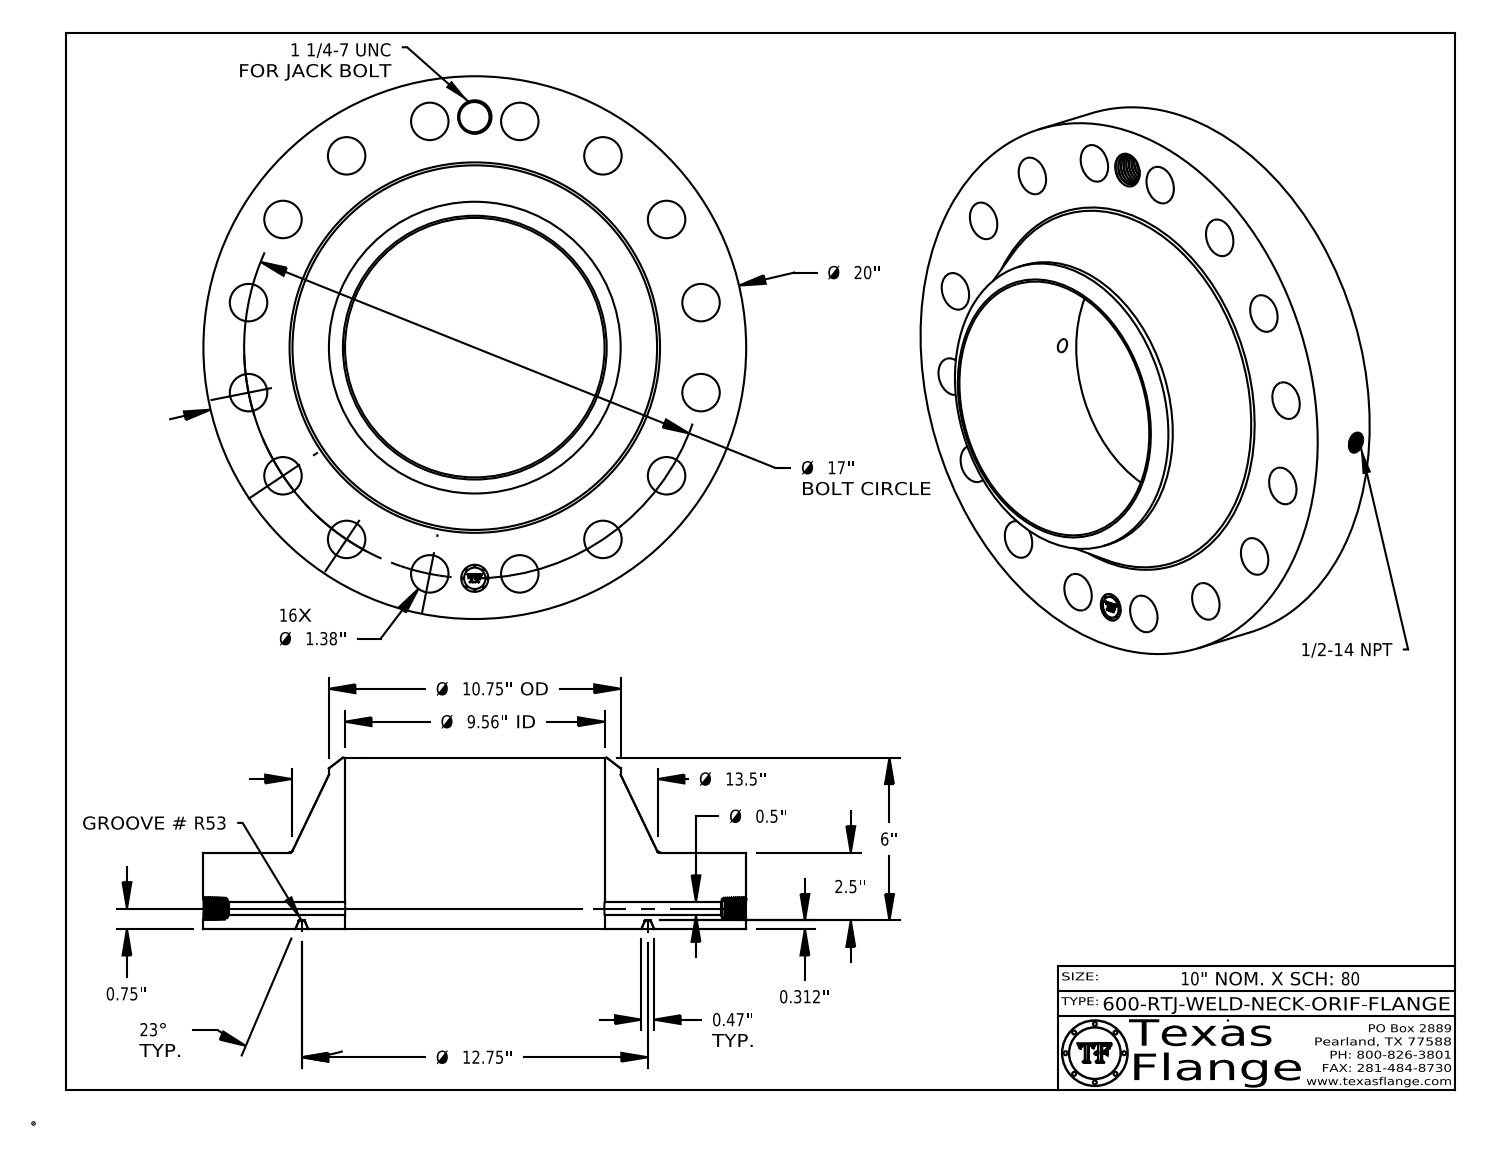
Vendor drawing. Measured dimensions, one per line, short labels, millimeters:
name: 600-RTJ-WELD-NECK
written by: CATIA V5 STEP AP214 (AUTOMOTIVE_DESIGN)
unit: mm
bodies: 1 solid, 822 faces (370 planar, 117 cylindrical, 335 other)
size: 508 × 508 × 160.3
volume: 12 120 000 mm³; area: 727 100 mm²
holes: 16× ⌀35.1, 1× ⌀12.7, 1× ⌀17.1, 1× ⌀25.4, 1× ⌀28.2, 1× ⌀242.9
bosses: 8× ⌀1.5, 1× ⌀508, 1× ⌀273.1, 1× ⌀20
face distances: 71.4, 7.9, 63.5, 160.3, 152.4, 88.9, 71, 63.1, 0.4, 89.3
hole spacings: 215.9, 305.3, 398.9, 423.5, 84.3, 239.9, 359, 431.8
